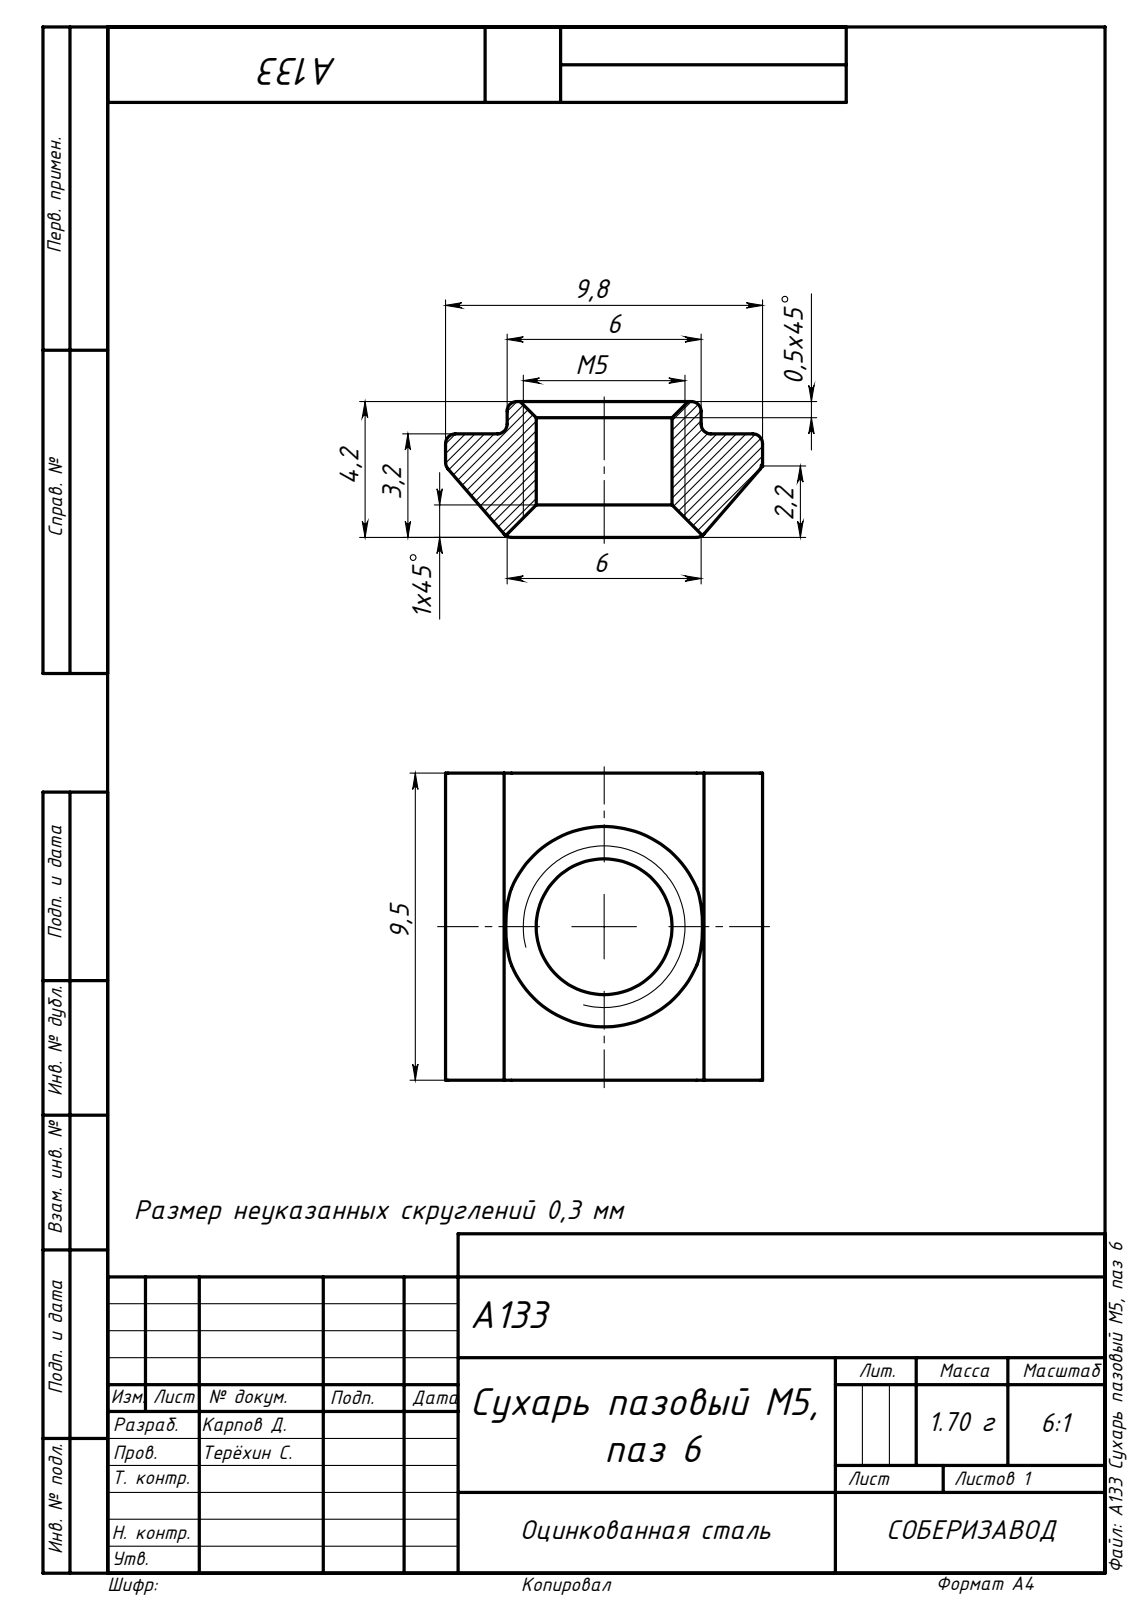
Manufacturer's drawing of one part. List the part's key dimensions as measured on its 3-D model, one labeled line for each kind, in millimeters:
Part name (STEP PRODUCT): A133 Сухарь пазовый М5, паз 6
STEP written by: SolidWorks 2019 (AUTOMOTIVE_DESIGN)
Units: millimetres
Bodies: 1 solid, 29 faces (13 planar, 12 cylindrical, 4 other)
Overall size (bounding box): 9.8 × 9.5 × 4.2
Volume: 247 mm³ · Surface area: 319 mm²
Round holes (diameter × count): ⌀4.2 ×1
Partial cylindrical surfaces — rounded edges, fillets, slot ends (radius × count): R0.3 ×10
Main face-to-face distances: 9.5, 4.2, 1, 3.2, 1.9, 7.9, 9.8, 6
